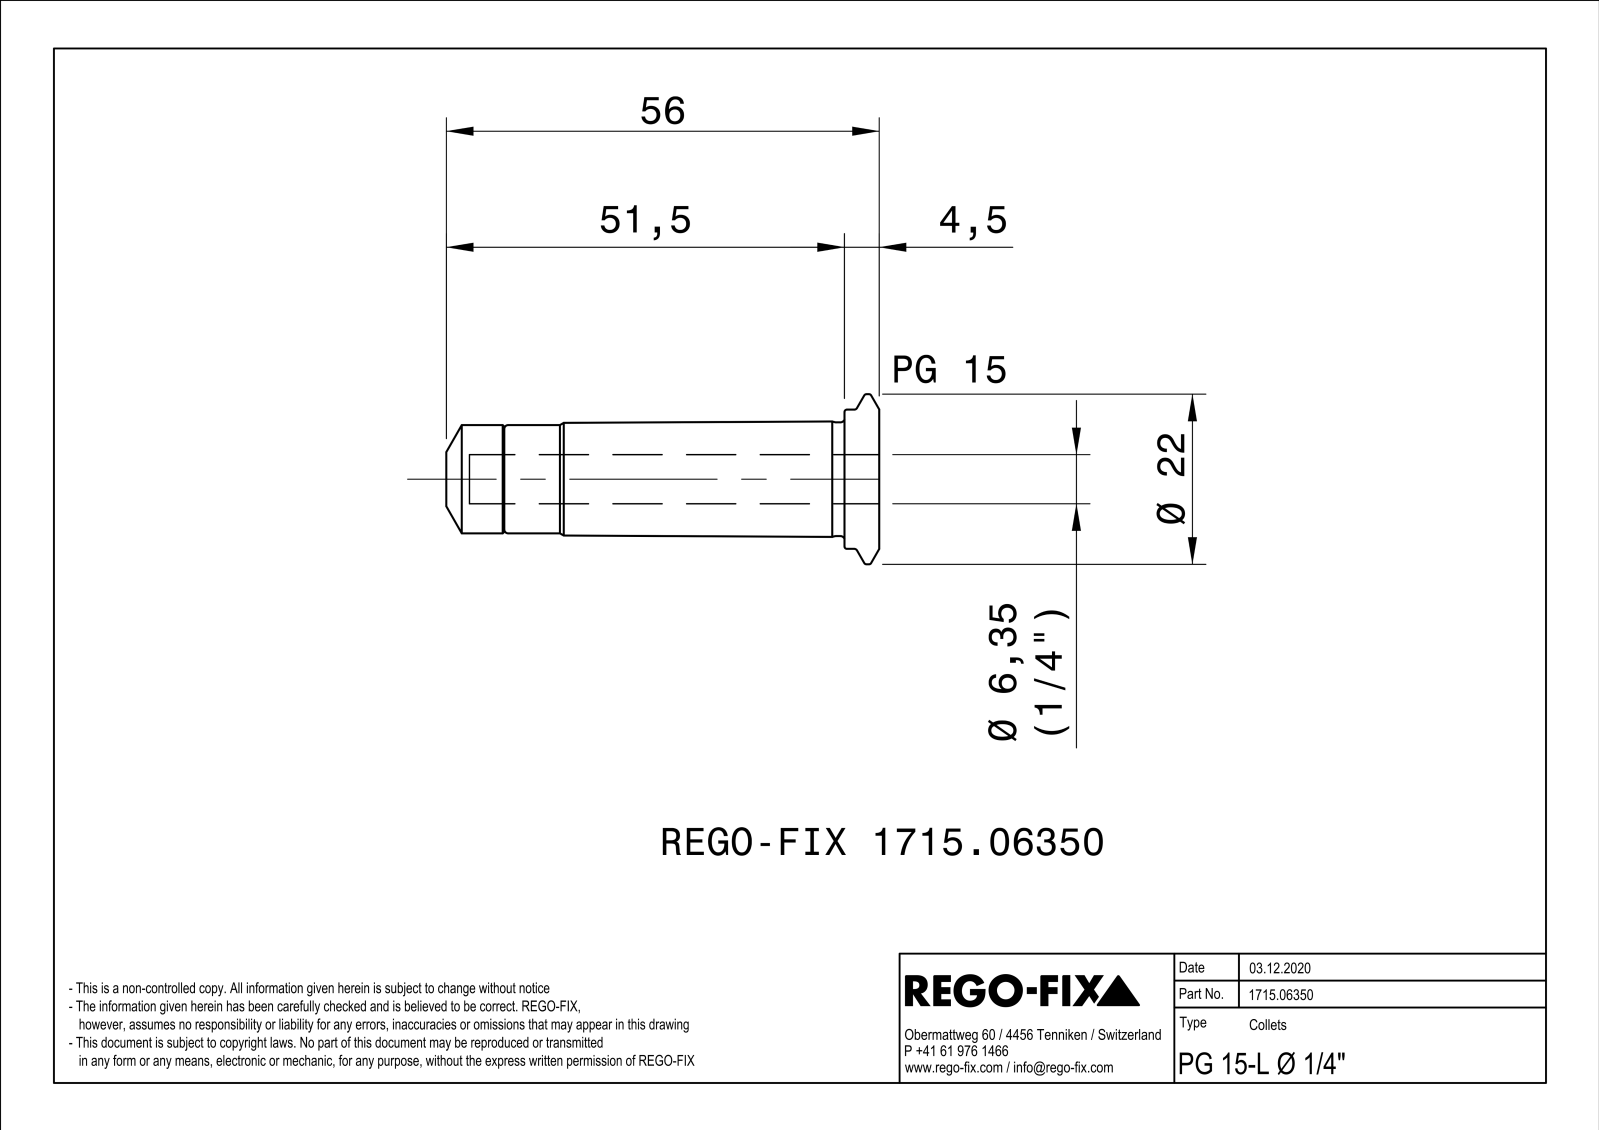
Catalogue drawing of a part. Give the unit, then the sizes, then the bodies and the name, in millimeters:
Units: millimetres
Overall size (bounding box): 56 × 22 × 21.99
Round holes (diameter × count): ⌀2.8 ×1, ⌀6.35 ×1, ⌀8.5 ×1, ⌀9.2 ×1, ⌀10.92 ×1, ⌀12.2 ×1
Round bosses / shafts (diameter × count): ⌀22 ×1, ⌀18 ×1, ⌀14.7 ×1, ⌀14 ×1, ⌀12 ×1, ⌀10.4 ×1
Partial cylindrical surfaces — rounded edges, fillets, slot ends (radius × count): R0.5 ×6, R2 ×3
Main face-to-face distances: 1, 48.5, 56, 7.5, 4.5, 44, 51.5, 42.8, 38.3, 5.7
Volume: 803 mm³ · Surface area: 5 744 mm²
Bodies: 1 solid, 97 faces (24 planar, 28 cylindrical, 45 other)
Part name (STEP PRODUCT): 0016441
STEP written by: SIEMENS PLM Software Solid Edge ST10 (AUTOMOTIVE_DESIGN)
